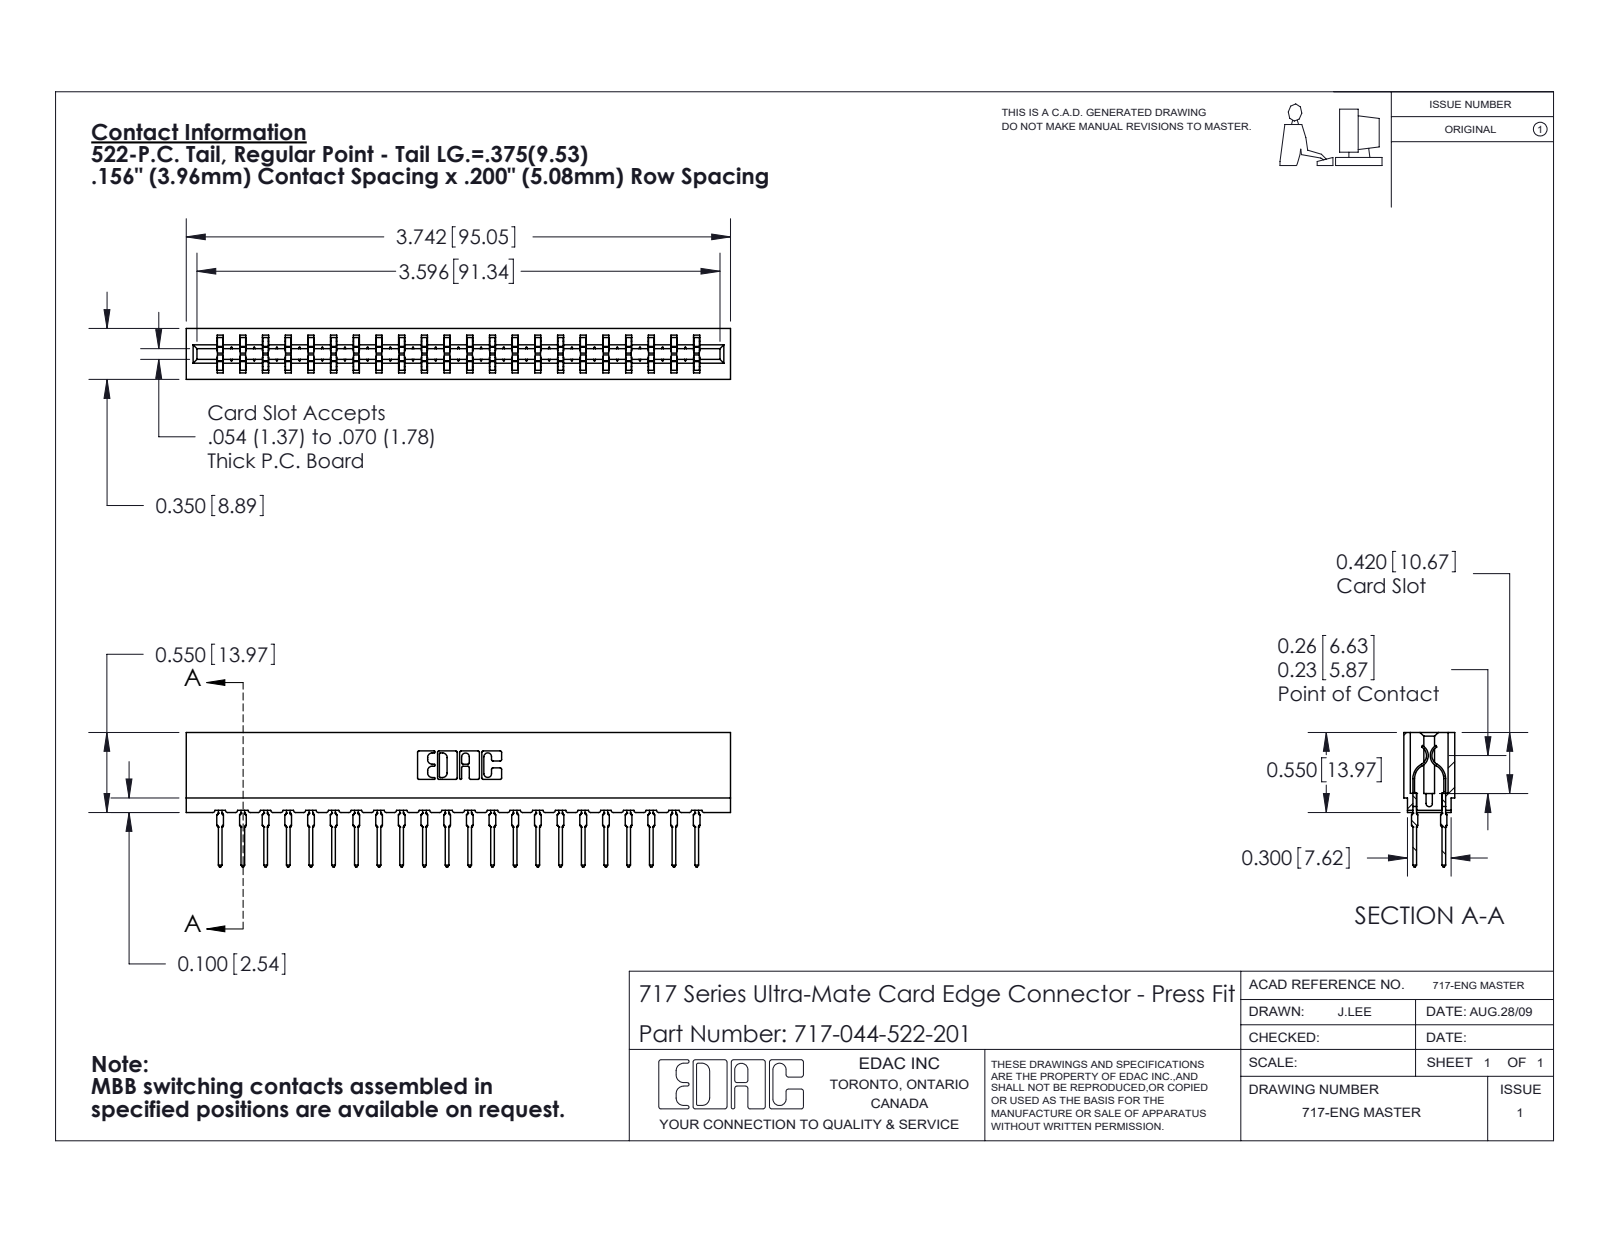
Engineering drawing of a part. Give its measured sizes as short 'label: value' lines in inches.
name: 717 Part_Insulator Option - 06; 745-292-001_522; 717-044-522-201
written by: SolidWorks 2020 (CONFIG_CONTROL_DESIGN)
unit: in
bodies: 45 solids, 4054 faces (2100 planar, 810 cylindrical, 1144 other)
size: 3.742 × 0.924 × 0.35
volume: 0.51 in³; area: 19.69 in²
rounds: 88× R0.021, 44× R0.015, 22× R0.01, 8× R0.005, 8× R0.011, 6× R0.007, 6× R0.031, 3× R0.026
face distances: 0.212, 0.138, 0.35, 0.063, 0.287, 0.076, 0.149, 0.156, 0.074, 0.624
